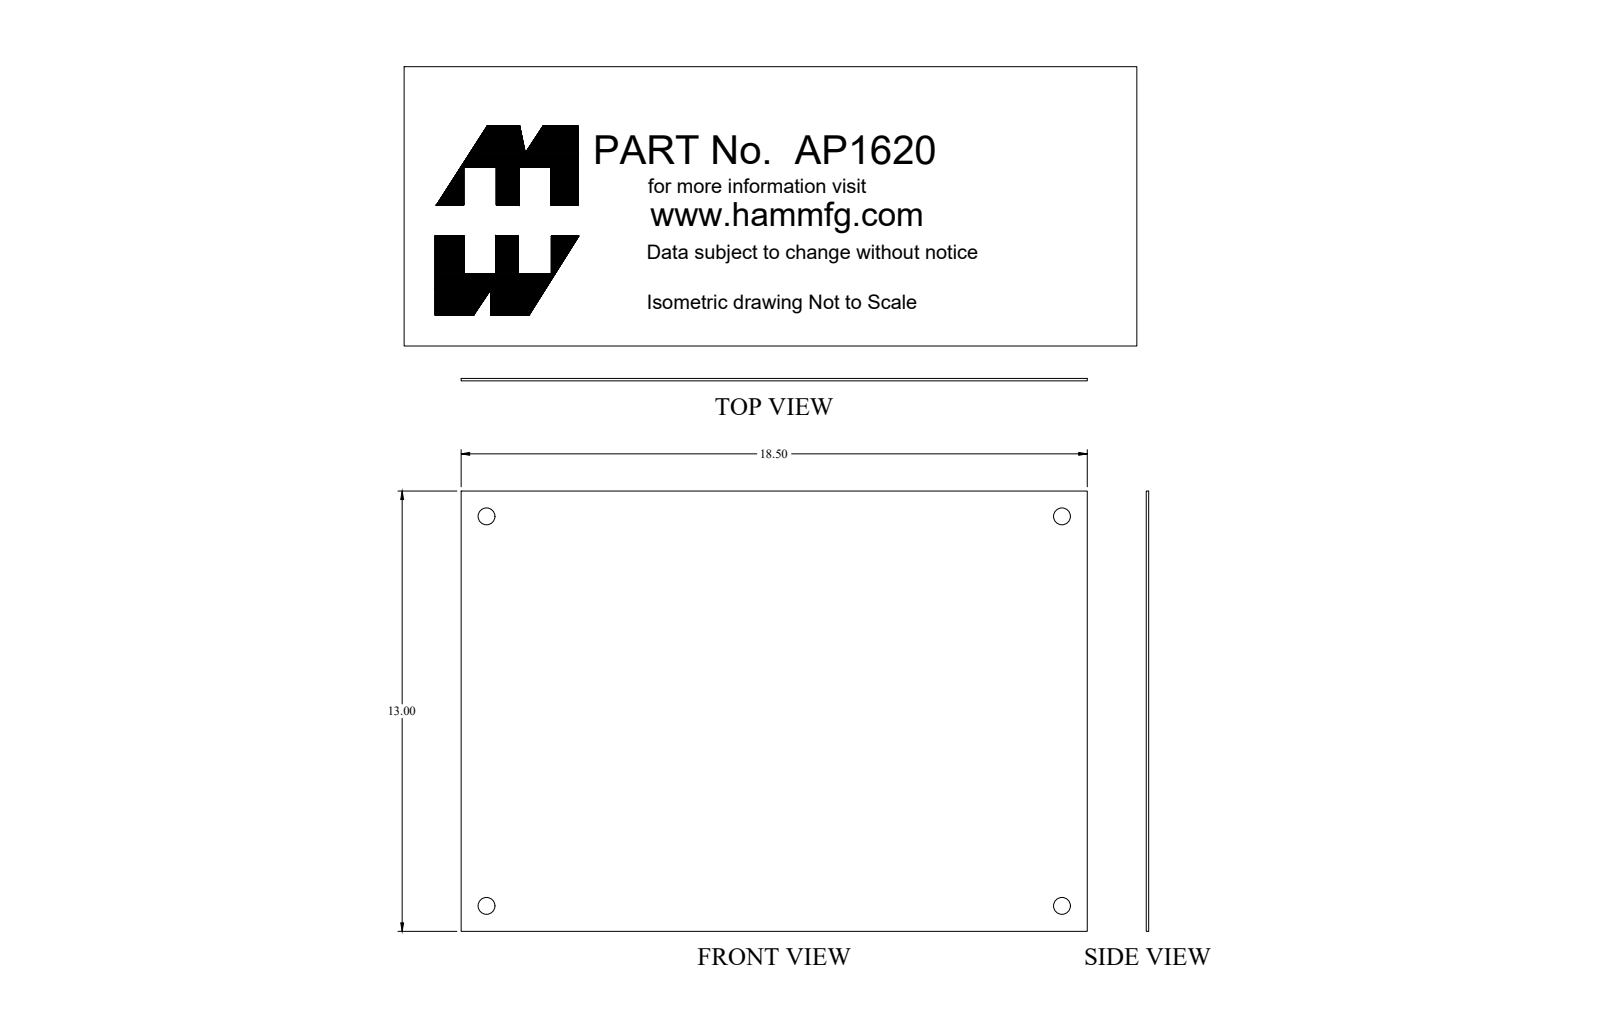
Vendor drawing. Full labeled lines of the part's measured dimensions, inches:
Part name (STEP PRODUCT): AP1620_Default
STEP written by: SolidWorks 2019 (CONFIG_CONTROL_DESIGN)
Units: inches
Bodies: 1 solid, 14 faces (6 planar, 8 cylindrical, 0 other)
Overall size (bounding box): 18.5 × 13 × 0.072
Volume: 17.26 in³ · Surface area: 484.4 in²
Round holes (diameter × count): ⌀0.5 ×4
Main face-to-face distances: 0.072, 13, 18.5
Hole centre spacings: 11.5, 17, 20.524
